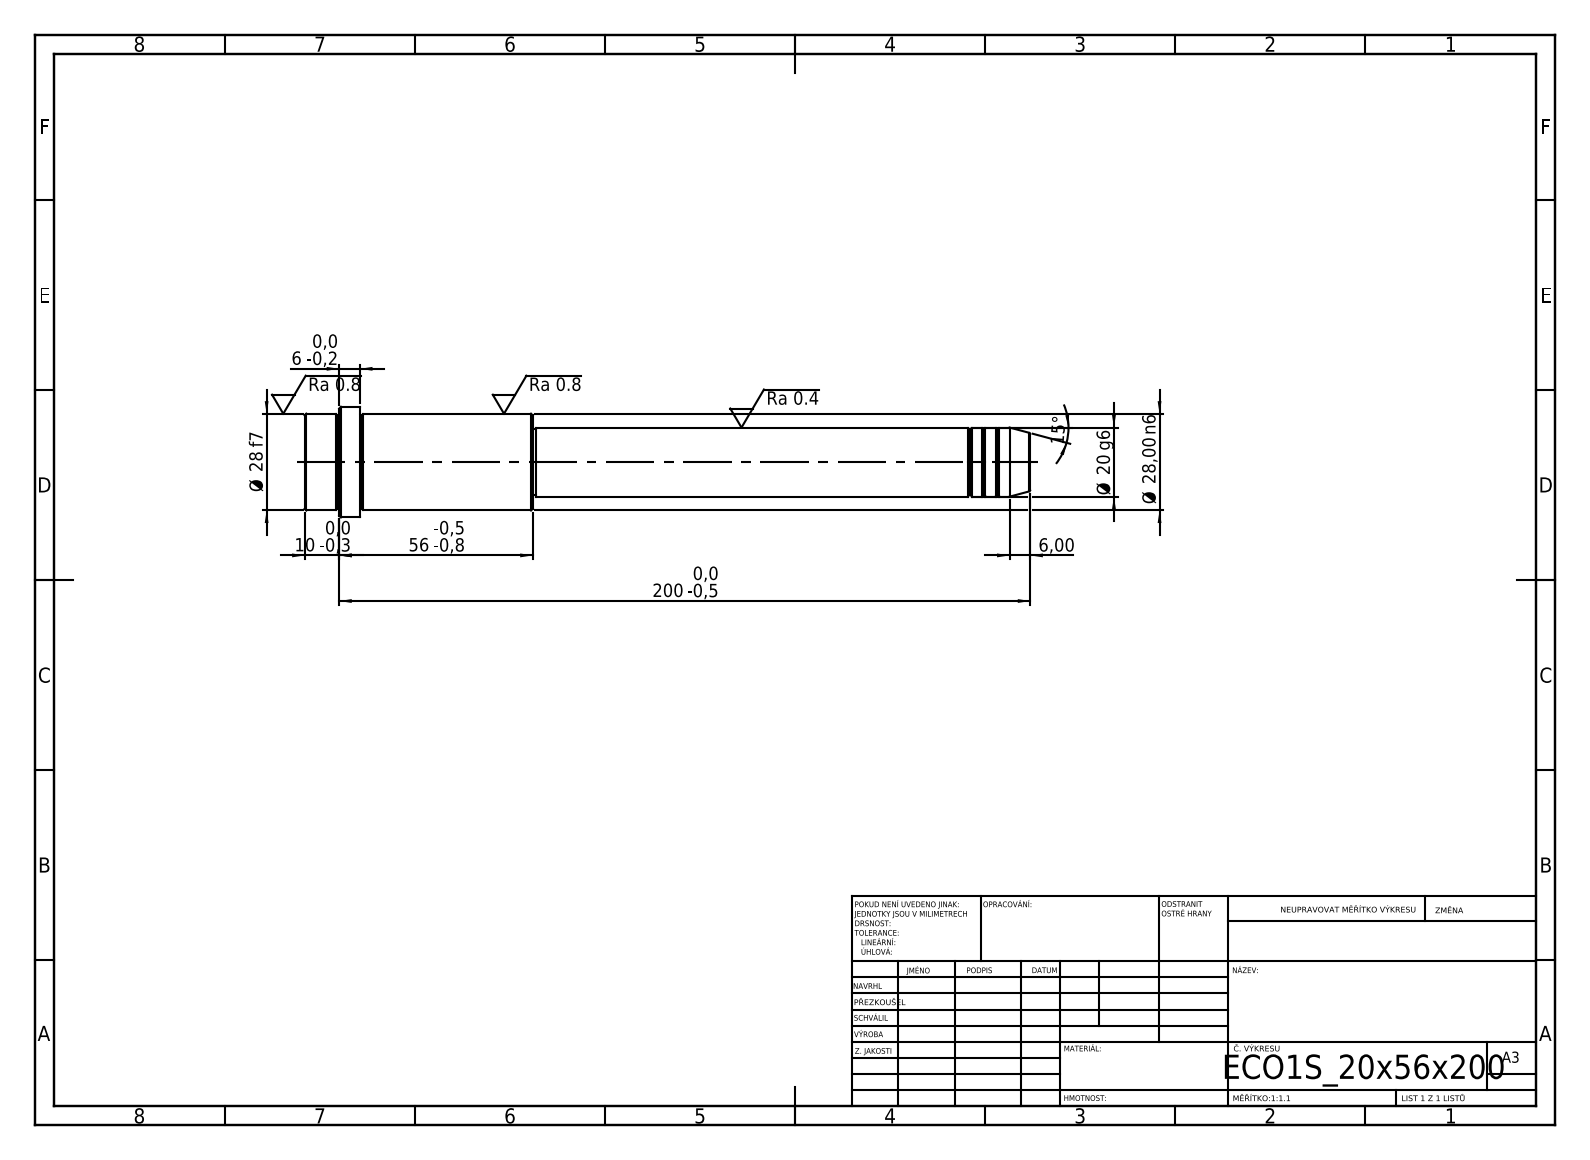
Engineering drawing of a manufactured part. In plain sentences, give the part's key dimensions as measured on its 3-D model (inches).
Its 3-D file was written by "SolidWorks 2019 (CONFIG_CONTROL_DESIGN)". It is 1 solid with 52 faces: 6 planar, 16 cylindrical and 30 other. Overall it measures 8.268 by 1.26 by 1.26 inches. Its volume is 5.28 cubic inches and its surface area 25.71 square inches. Round bosses or shafts: 1 of diameter 1.26, 1 of diameter 1.102, 1 of diameter 0.787, 1 of diameter 0.748. The main face-to-face distances are 2.598, 5.669, 8.268, 7.638, 1.969, 0.63, 7.874, 2.205, 0.236, 0.394.
